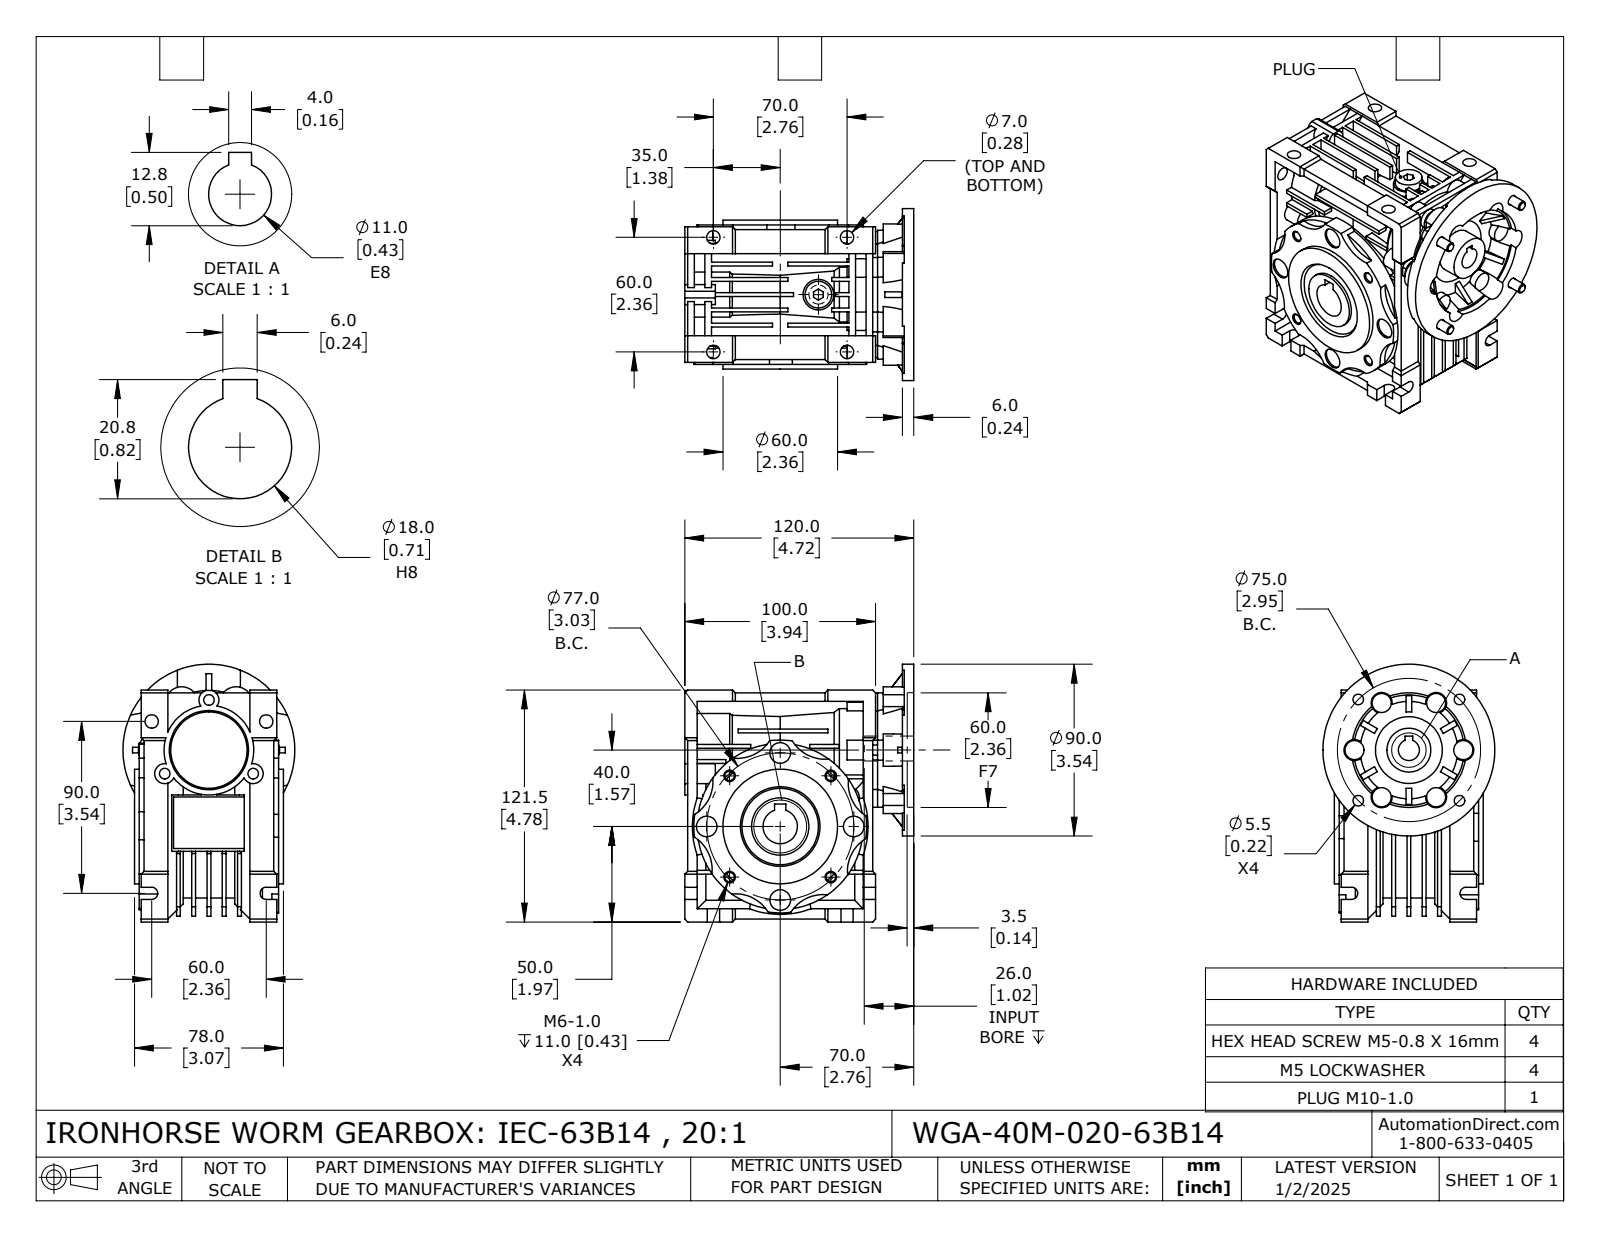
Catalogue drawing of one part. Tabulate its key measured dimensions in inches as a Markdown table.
| quantity | value |
| --- | --- |
| part name | WGA-40M-020-63B14 |
| STEP written by | SolidWorks 2024 (CONFIG_CONTROL_DESIGN) |
| units | inches |
| bodies | 14 solids, 1003 faces (564 planar, 307 cylindrical, 132 other) |
| overall size | 5.315 × 5.028 × 3.543 |
| volume | 40.72 in³ |
| surface area | 252.8 in² |
| round holes (diameter × count) | 0.276 × 6, 0.194 × 4, 0.201 × 4, 0.217 × 4, 0.425 × 4, 0.219 × 3, 0.354 × 1, 0.433 × 1, 0.453 × 1, 0.709 × 1, 0.906 × 1, 1.102 × 1 |
| round bosses / shafts (diameter × count) | 0.394 × 6, 0.362 × 4, 0.197 × 4, 3.543 × 1, 2.953 × 1, 2.362 × 1, 2.126 × 1, 1.85 × 1 |
| partial cylindrical surfaces (radius × count) | 0.207 × 9, 0.787 × 8, 0.126 × 6, 0.206 × 6, 0.217 × 6, 0.335 × 6, 0.217 × 4, 1.181 × 1 |
| main face-to-face distances | 0.315, 0.236, 0.079, 0.059, 0.63, 0.394, 0.197, 0.551, 0.098, 0.748 |
| hole center spacings | 1.146, 1.476, 2.088, 2.765, 1.32, 1.516, 2.144, 2.953 |
